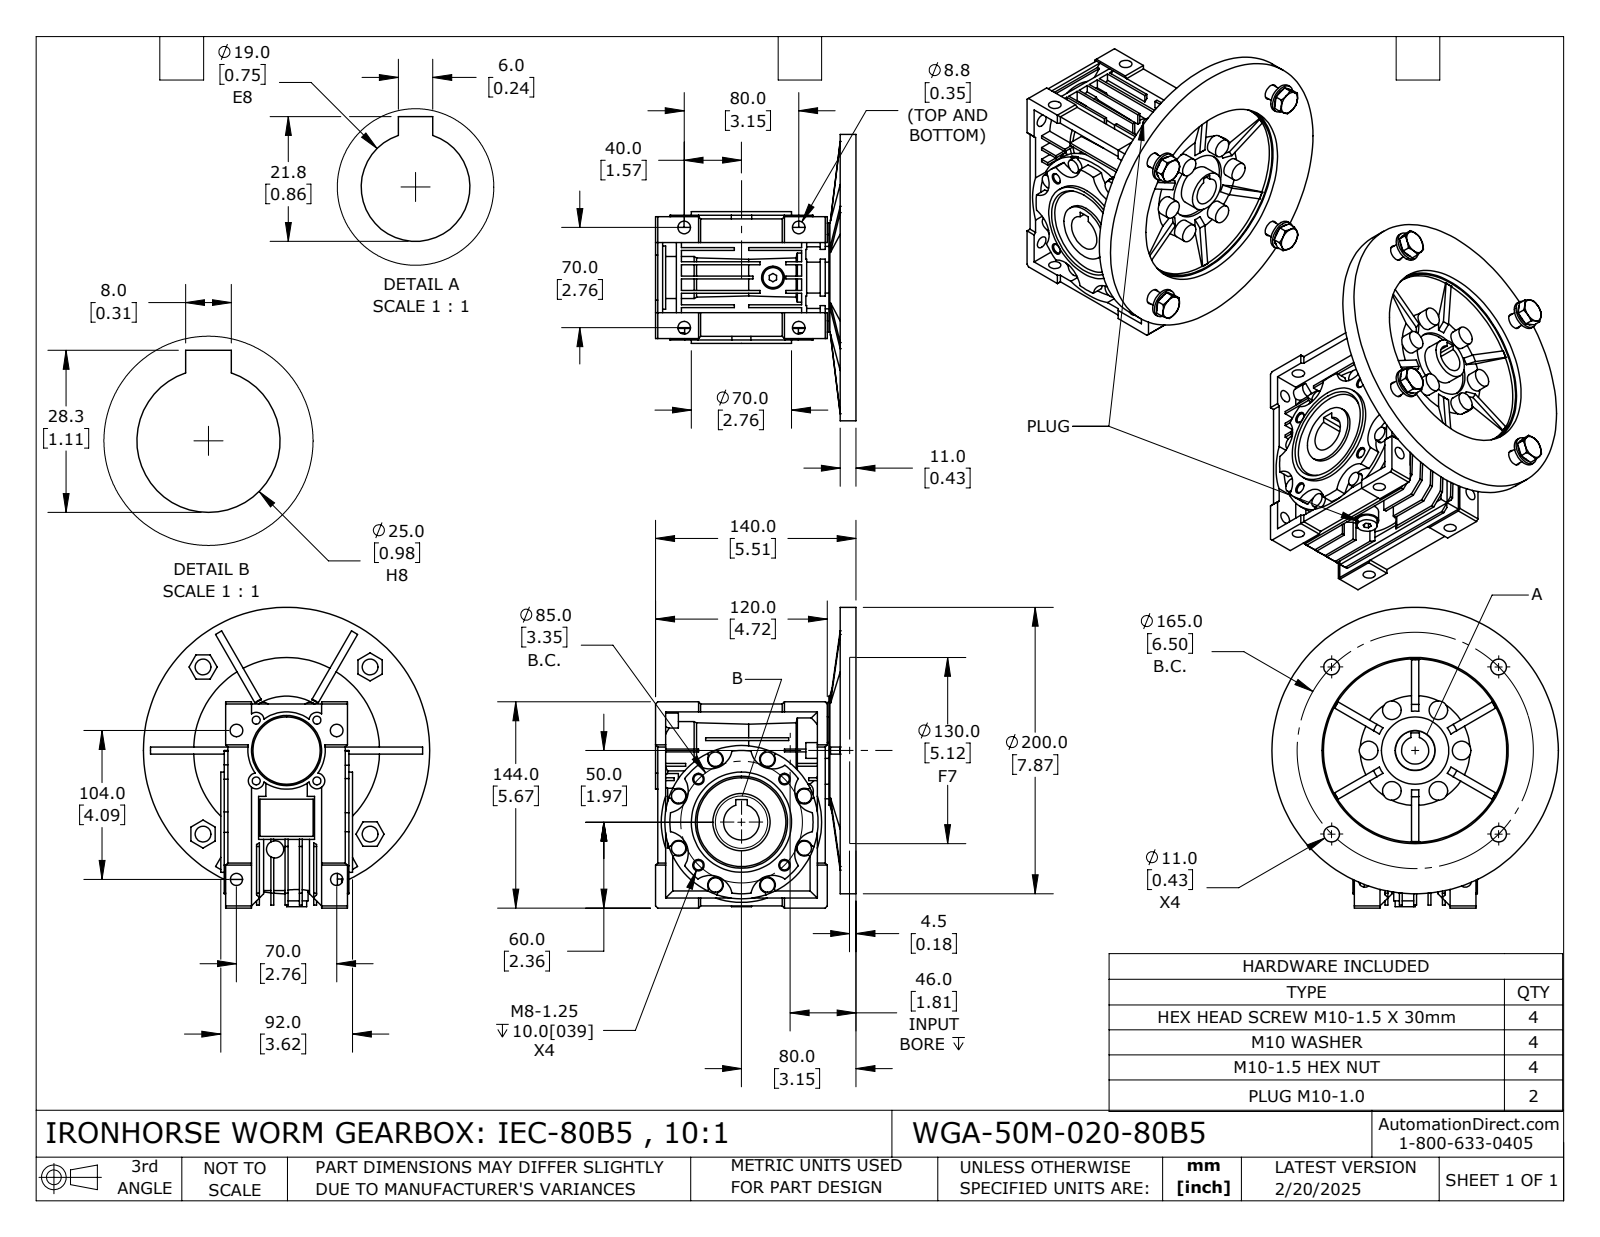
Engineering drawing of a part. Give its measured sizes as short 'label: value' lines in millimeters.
name: WGA-50M-020-80B5
written by: SolidWorks 2024 (CONFIG_CONTROL_DESIGN)
unit: mm
bodies: 19 solids, 1273 faces (701 planar, 364 cylindrical, 208 other)
size: 210 × 200 × 158.43
volume: 1 274 000 mm³; area: 298 738 mm²
holes: 10× ⌀8.5, 8× ⌀8.8, 4× ⌀5.55, 4× ⌀10, 4× ⌀10.5, 4× ⌀11, 2× ⌀6.65, 2× ⌀6.65, 2× ⌀9, 1× ⌀19, 1× ⌀20, 1× ⌀25
bosses: 8× ⌀10, 6× ⌀16, 6× ⌀13, 4× ⌀20, 2× ⌀14, 2× ⌀9.8, 2× ⌀8.3, 1× ⌀200
rounds: 18× R5.5, 8× R6, 8× R15, 8× R15.5, 1× R20.76, 1× R46, 1× R47.7, 1× R50
face distances: 11, 8, 10, 2, 1.5, 7, 5.5, 20, 5, 55
hole spacings: 87.79, 70, 30, 42.42, 42.5, 52.51, 60.1, 82.51
